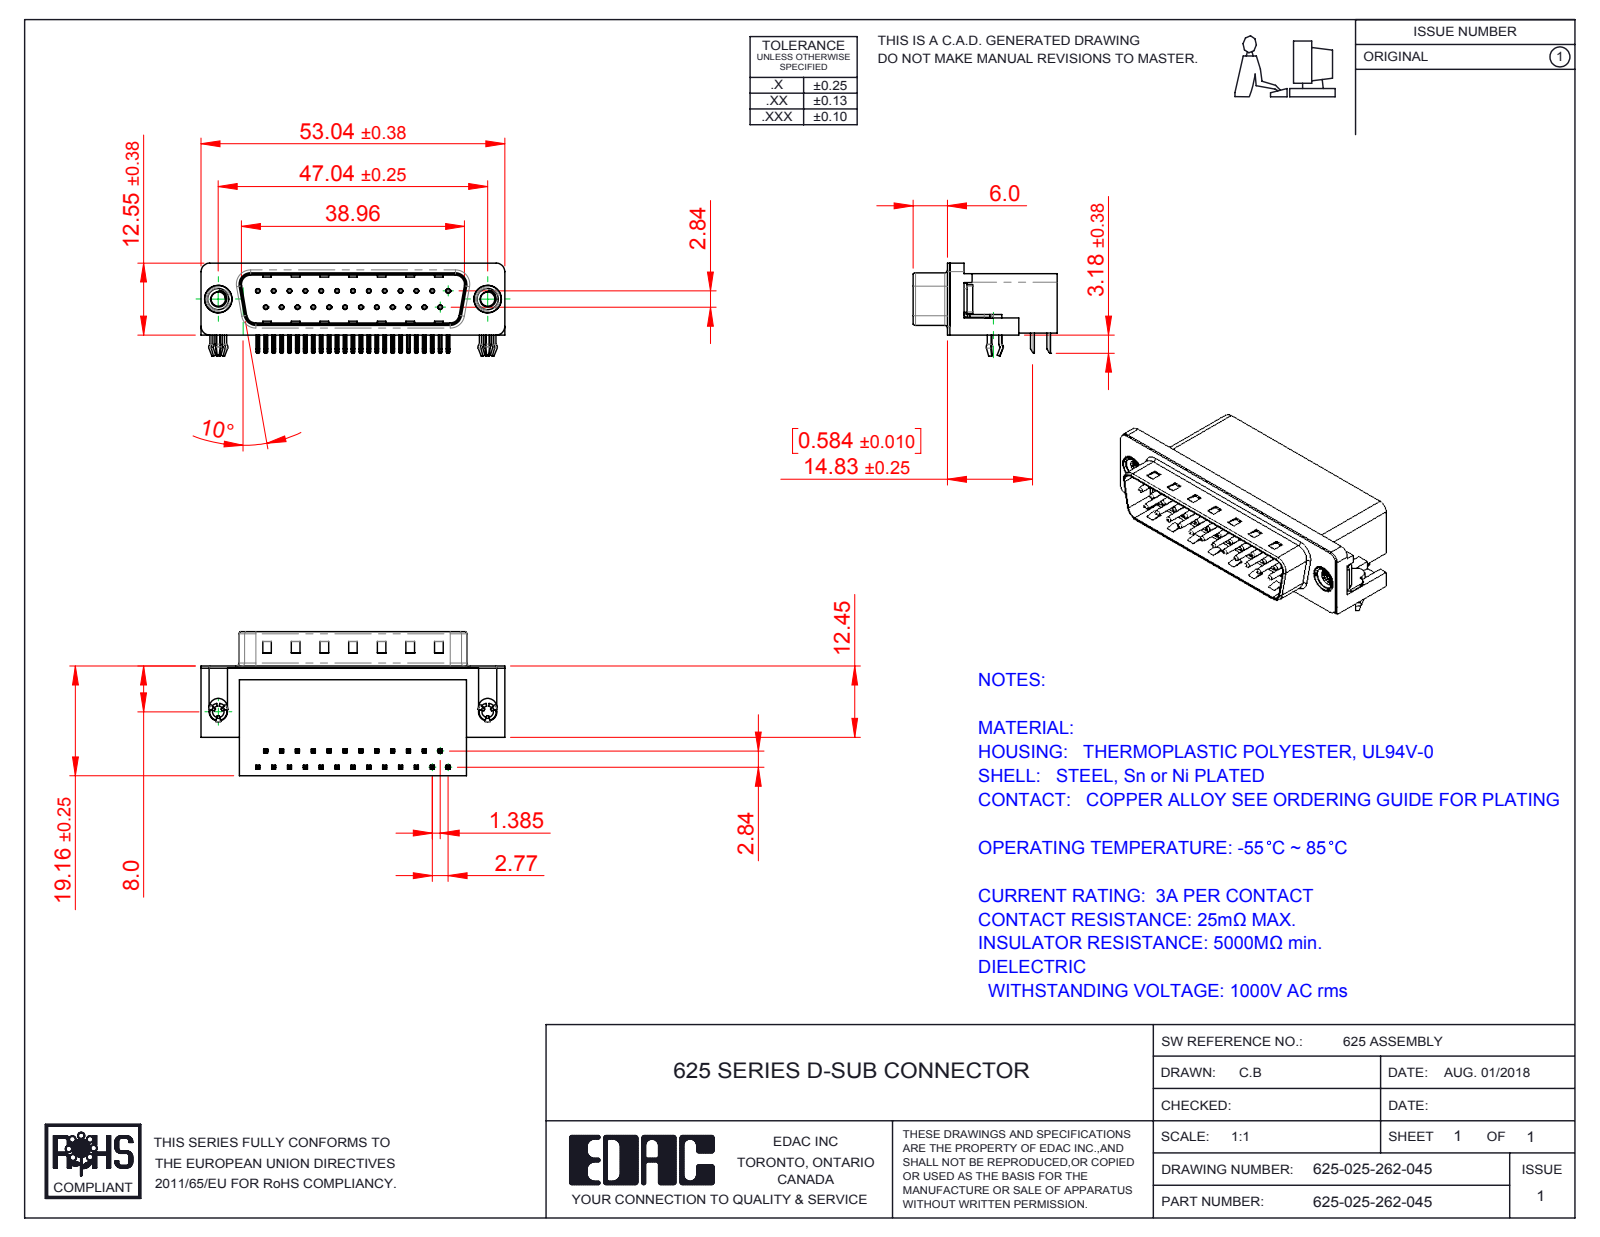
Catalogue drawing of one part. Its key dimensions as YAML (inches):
part_name: "625 M3 Threaded Rivet; 625 Contact Top; 625 Contact Bottom; 625 Shell_25 Socket (+3 more)"
step_written_by: "SolidWorks 2016 (CONFIG_CONTROL_DESIGN)"
units: inches
bodies: {solids: 31, faces: 2369, planar: 1443, cylindrical: 671, other: 255}
overall_size: [2.088, 0.991, 0.64]
volume: 0.559
surface_area: 13.84
round_holes:
  - {diameter: 0.014, count: 25}
  - {diameter: 0.031, count: 25}
  - {diameter: 0.079, count: 2}
  - {diameter: 0.098, count: 2}
  - {diameter: 0.157, count: 2}
  - {diameter: 0.189, count: 2}
  - {diameter: 0.197, count: 2}
round_bosses_or_shafts:
  - {diameter: 0.03, count: 25}
  - {diameter: 0.193, count: 2}
  - {diameter: 0.187, count: 2}
  - {diameter: 0.154, count: 2}
  - {diameter: 0.118, count: 2}
partial_cylinders:
  - {radius: 0.01, count: 112}
  - {radius: 0.005, count: 50}
  - {radius: 0.039, count: 16}
  - {radius: 0.02, count: 9}
  - {radius: 0.063, count: 8}
  - {radius: 0.059, count: 7}
  - {radius: 0.035, count: 4}
  - {radius: 0.079, count: 4}
face_to_face_distances: [0.016, 0.407, 0.739, 0.083, 0.345, 0.412, 0.428, 0.067, 0.754, 0.398]
hole_center_spacings: [0.124, 0.109, 0.436, 0.218, 0.327, 0.198, 0.545, 0.294]
